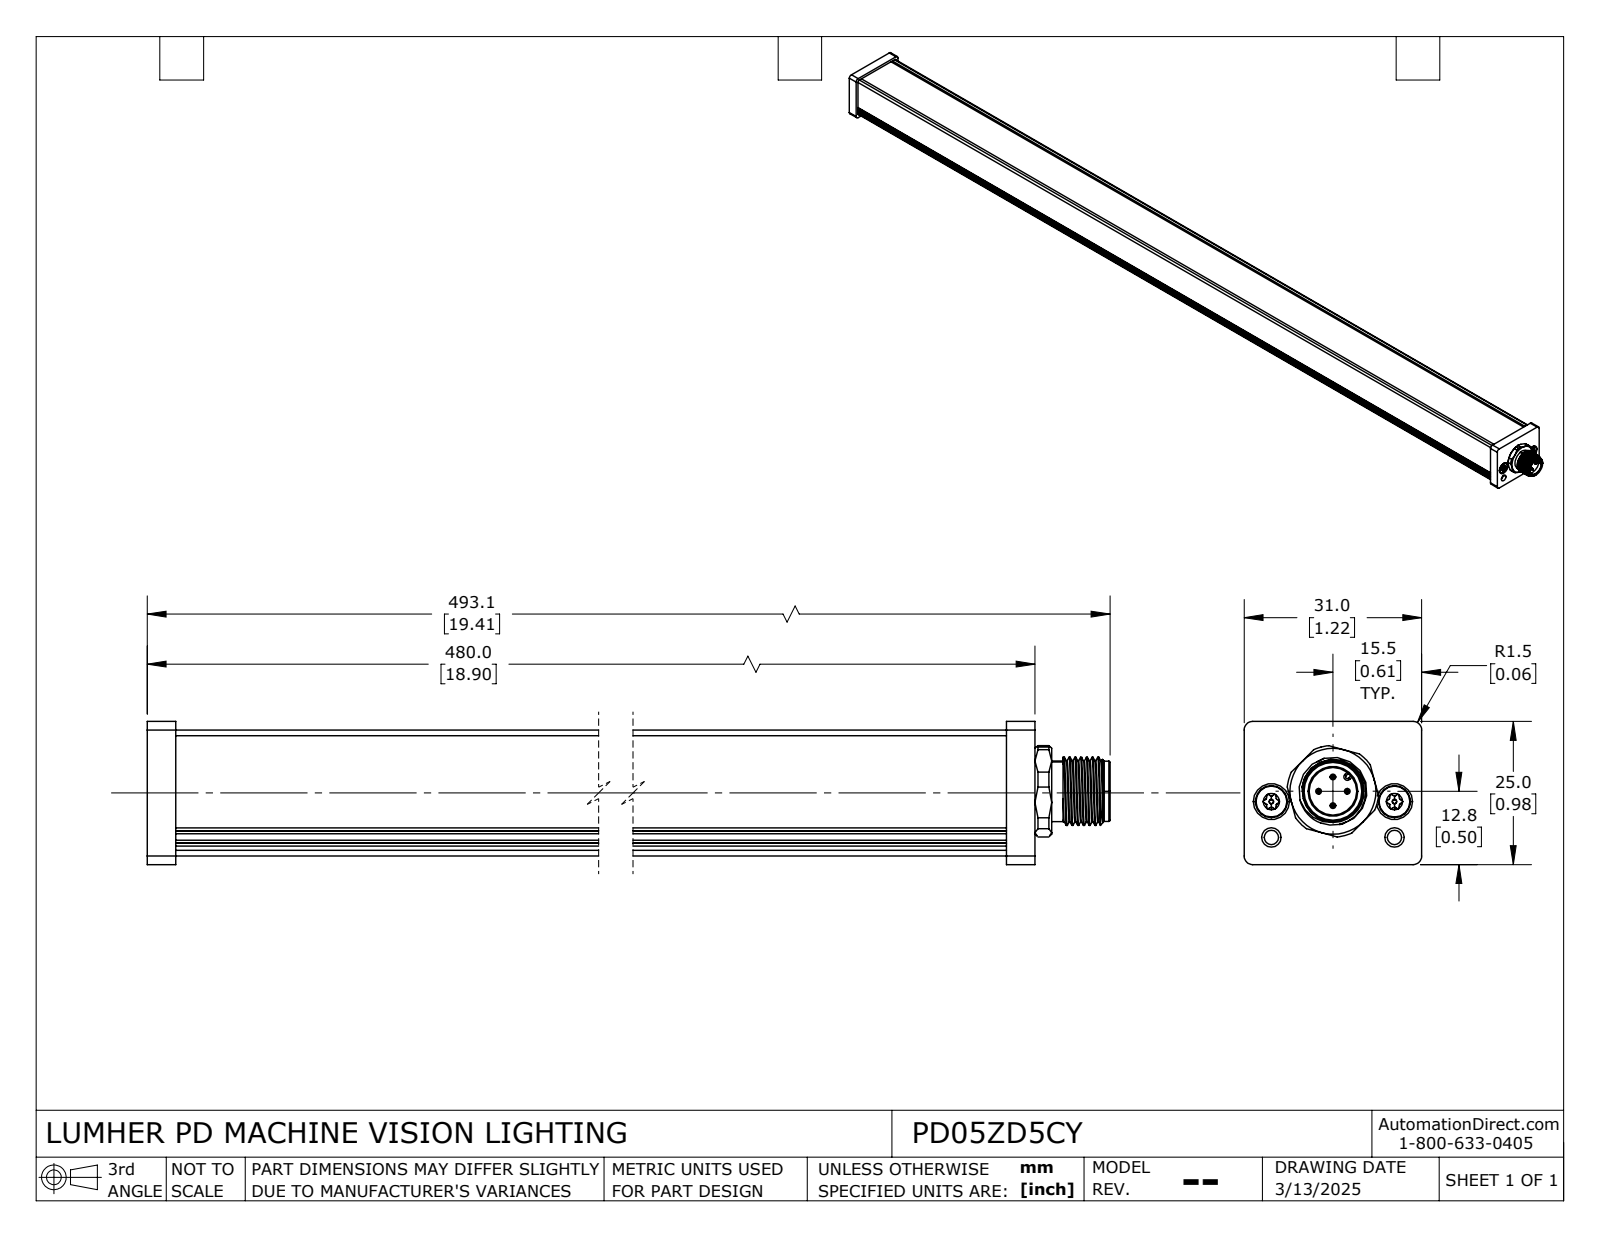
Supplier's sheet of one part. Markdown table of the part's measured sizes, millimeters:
| quantity | value |
| --- | --- |
| part name | PD05__5_Y |
| STEP written by | SolidWorks 2024 (AUTOMOTIVE_DESIGN) |
| units | millimeters |
| bodies | 1 solid, 563 faces (89 planar, 296 cylindrical, 178 other) |
| overall size | 493.1 × 31 × 25 |
| volume | 283 753 mm³ |
| surface area | 64 167 mm² |
| round holes (diameter × count) | 1.45 × 4, 3.4 × 4, 2.5 × 2, 8.3 × 1, 9.4 × 1 |
| round bosses / shafts (diameter × count) | 1.4 × 4, 1 × 4, 5.6 × 2, 3 × 2, 0.8 × 2, 11.9 × 1, 10.6 × 1, 10.5 × 1 |
| partial cylindrical surfaces (radius × count) | 0.57 × 24, 0.25 × 12, 0.5 × 8, 1 × 8, 3 × 6, 1.5 × 4, 0.3 × 2, 1.02 × 2 |
| main face-to-face distances | 28, 1, 1.5, 2, 22, 27, 3, 21.75, 2.5, 475 |
| hole center spacings | 2.5, 3.54, 5, 6.25, 8.44, 10.77, 10.9, 11.53 |
